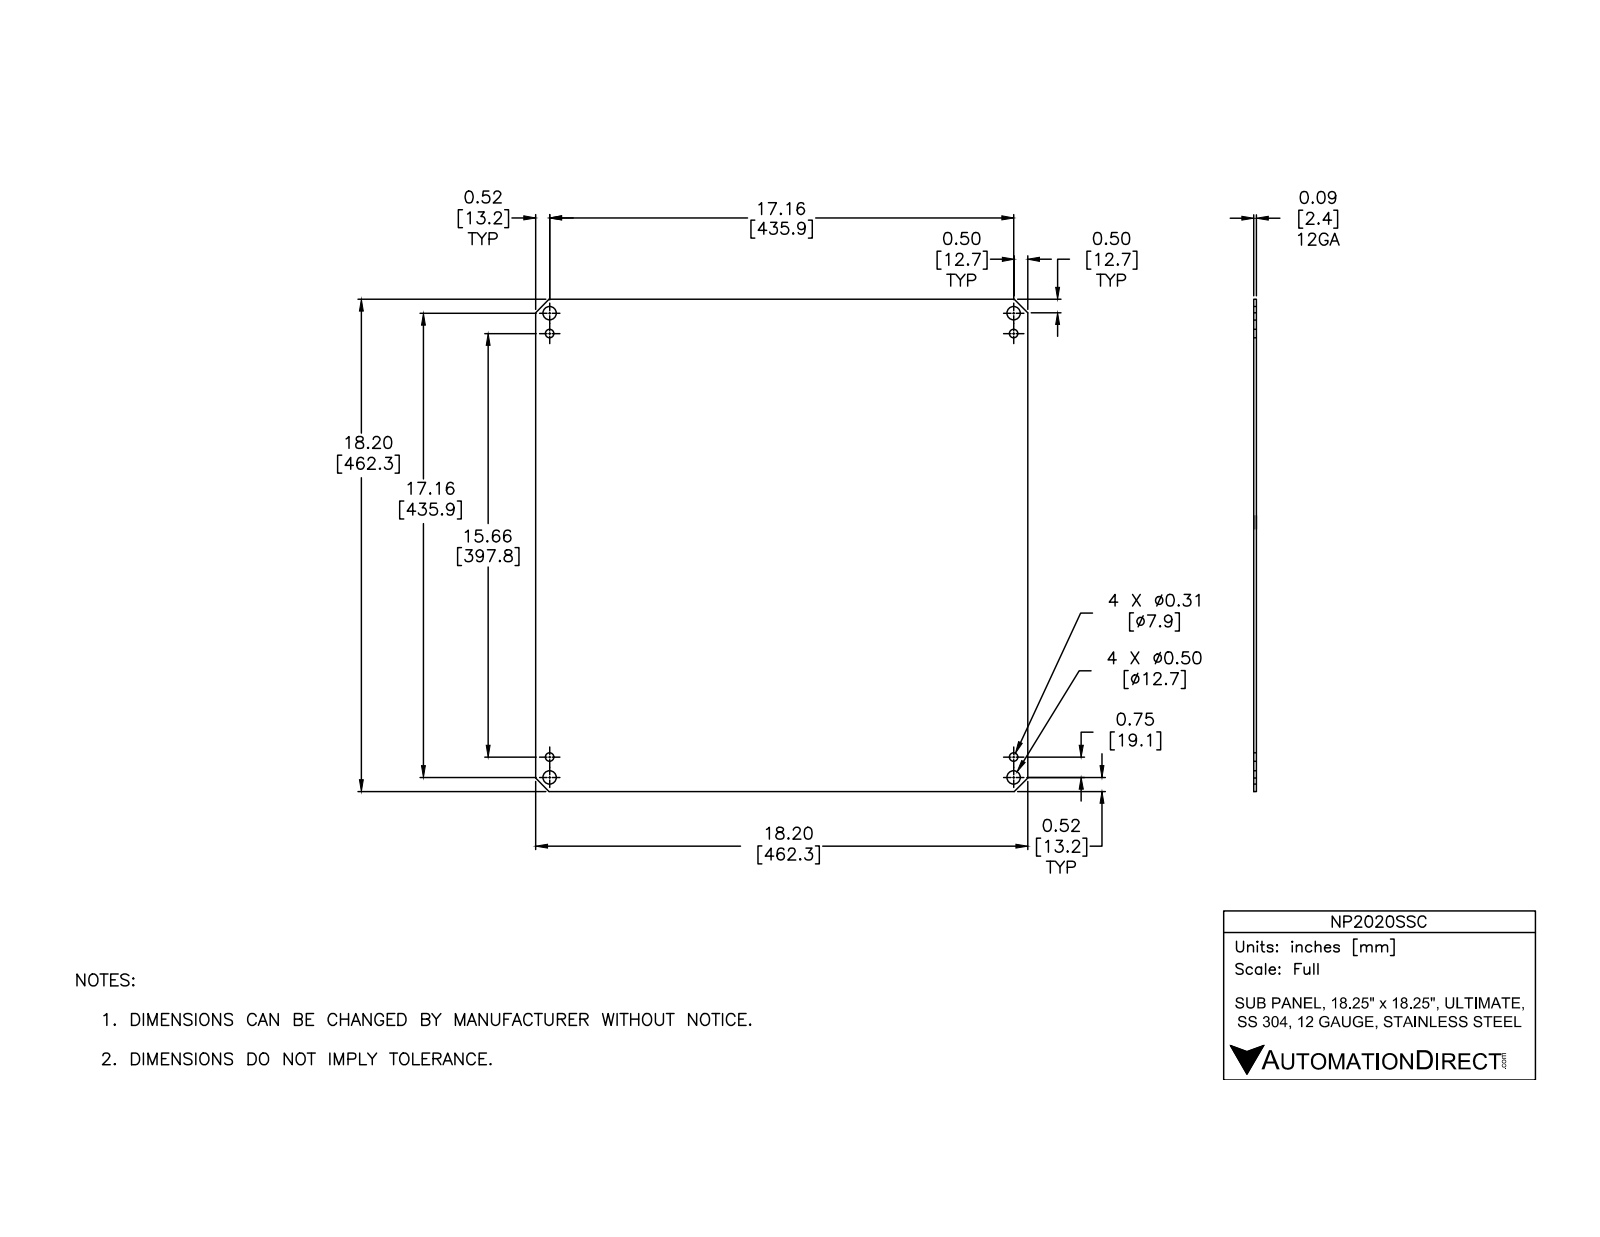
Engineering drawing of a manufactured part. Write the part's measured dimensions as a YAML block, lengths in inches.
part_name: "NP2020SSC"
step_written_by: "Autodesk Inventor 2012 (AUTOMOTIVE_DESIGN)"
units: inches
bodies: {solids: 1, faces: 18, planar: 10, cylindrical: 8, other: 0}
overall_size: [18.2, 18.2, 0.094]
volume: 30.9
surface_area: 667
round_holes:
  - {diameter: 0.313, count: 4}
  - {diameter: 0.5, count: 4}
face_to_face_distances: [0.094, 18.2, 25.028, 25.028]
hole_center_spacings: [17.16, 0.75, 16.41, 17.176, 23.743, 15.66, 23.231, 24.268]
